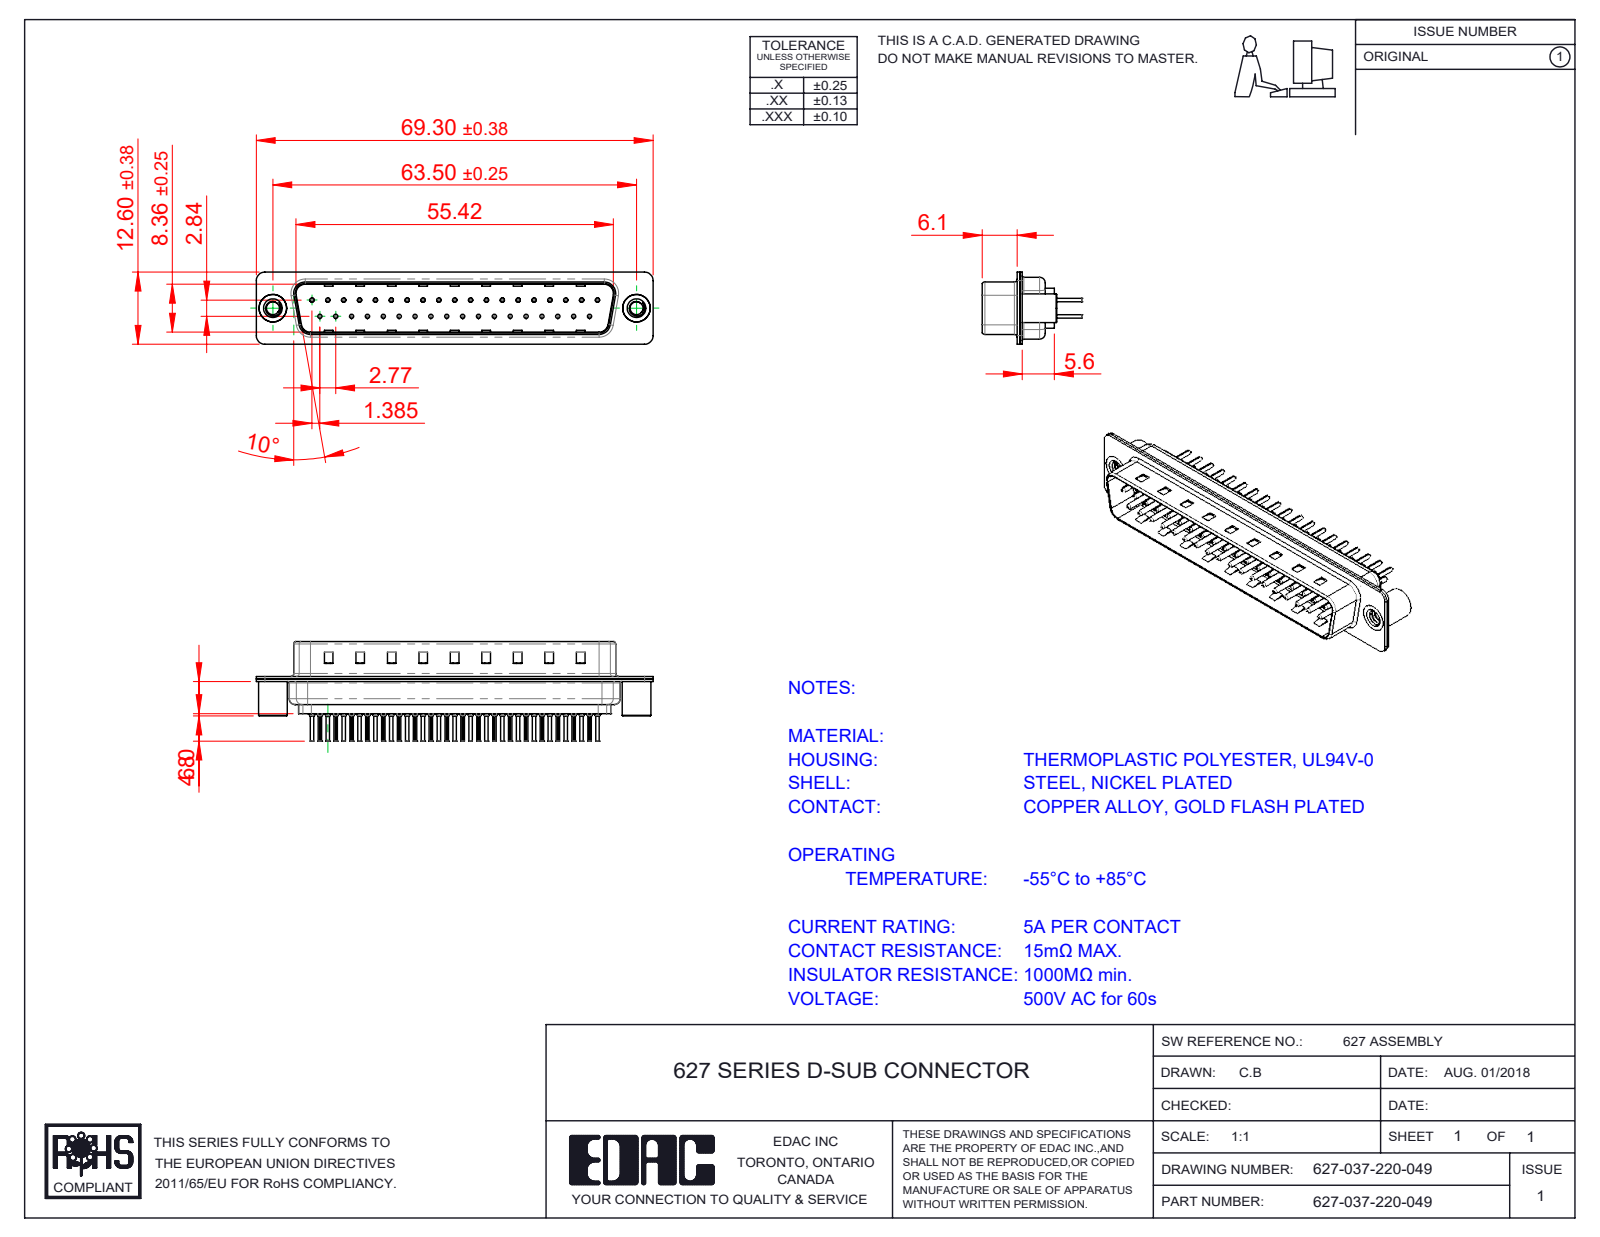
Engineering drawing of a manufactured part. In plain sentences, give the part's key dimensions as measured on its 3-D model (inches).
The part is named "627 Contact Row 1_20L; 627 Shell Front_37 Contacts; 627 Housing_37 LP; 627 4-40 Threaded Standoff BS (+3 more)". Its 3-D file was written by "SolidWorks 2020 (CONFIG_CONTROL_DESIGN)". It is 42 solids with 4060 faces: 1091 planar, 1530 cylindrical and 1439 other. Overall it measures 2.728 by 0.681 by 0.496 inches. Its volume is 0.232 cubic inches and its surface area 16.85 square inches. Round holes: 37 of diameter 0.008, 37 of diameter 0.014, 37 of diameter 0.043, 37 of diameter 0.063, 2 of diameter 0.089, 2 of diameter 0.157, 2 of diameter 0.189. Round bosses or shafts: 37 of diameter 0.079, 37 of diameter 0.059, 37 of diameter 0.03, 37 of diameter 0.024, 2 of diameter 0.197, 2 of diameter 0.193. Partial cylindrical surfaces (rounded edges, fillets, slot ends): 74 of radius 0.004, 16 of radius 0.059, 12 of radius 0.079, 8 of radius 0.02, 8 of radius 0.063, 4 of radius 0.01, 4 of radius 0.024, 4 of radius 0.026. The main face-to-face distances are 0.016, 0.032, 0.377, 0.018, 0.345, 0.059, 0.035, 0.055, 0.256, 0.238. The hole center spacings are 0.124, 0.109, 0.218, 0.327, 0.198, 0.398, 0.436, 0.503.
